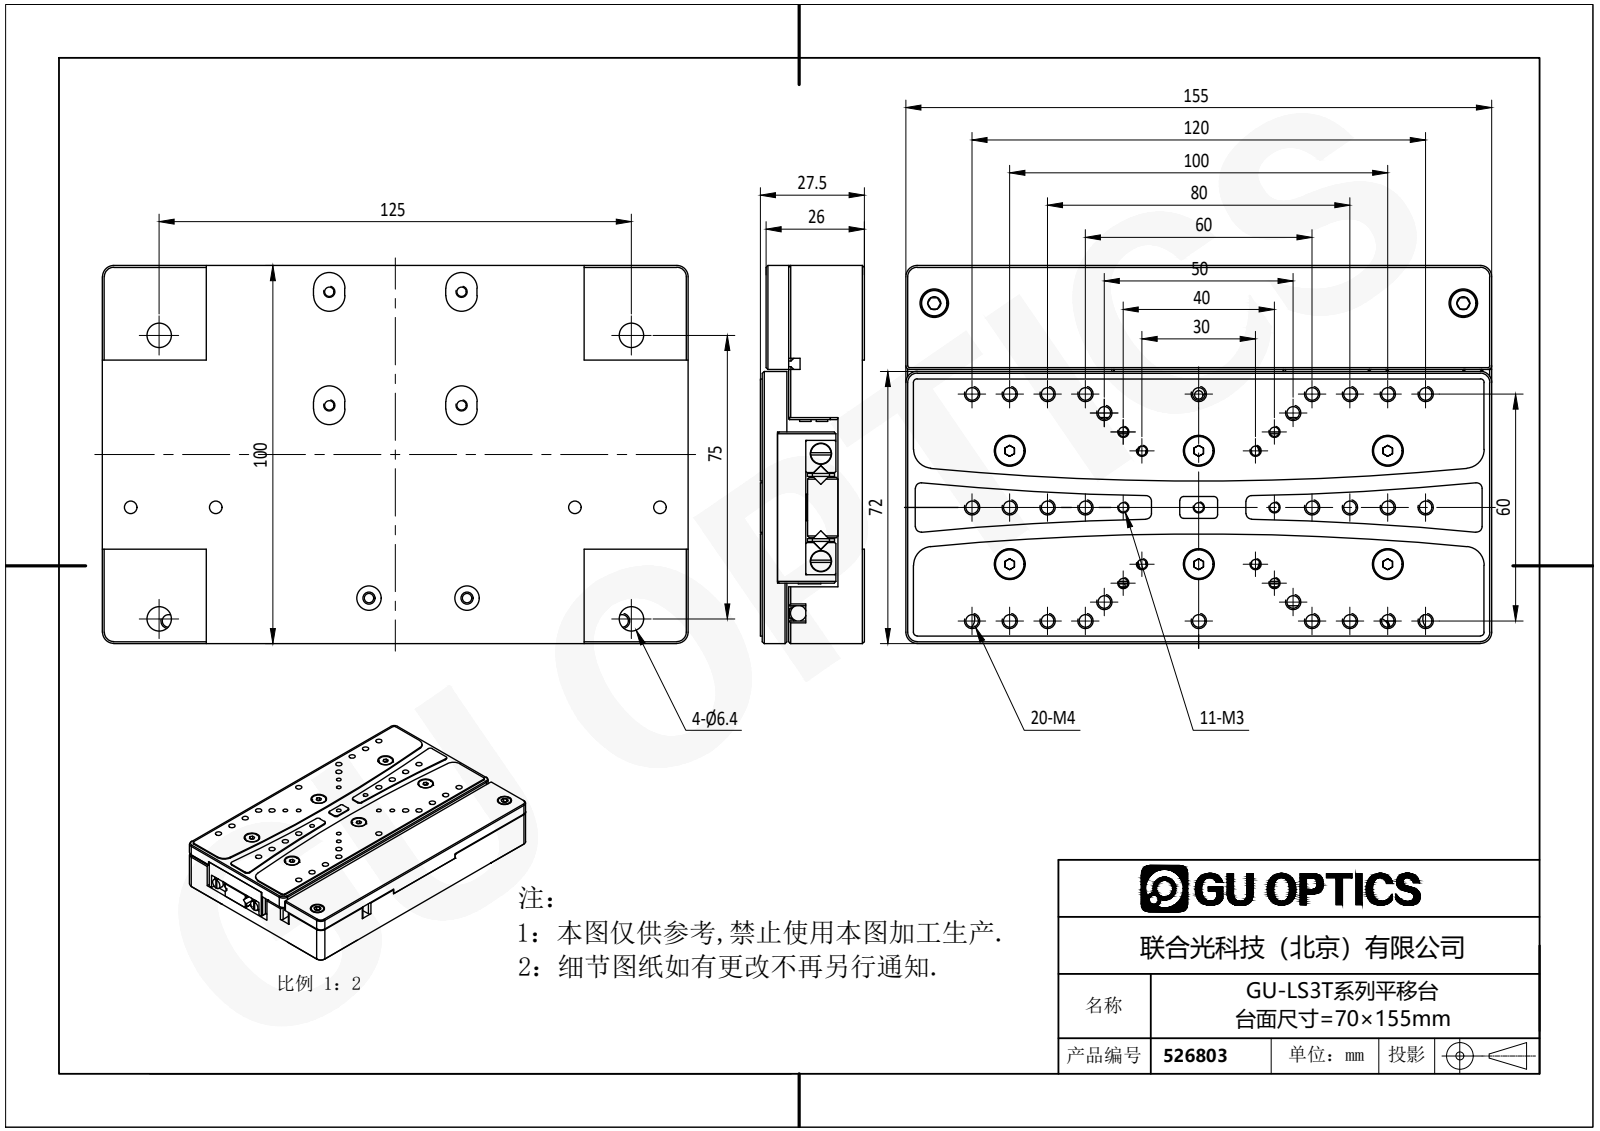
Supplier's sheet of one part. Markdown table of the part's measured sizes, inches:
| quantity | value |
| --- | --- |
| part name | GU-LS3T系列平移台 台面尺寸=70×155mm |
| STEP written by | SolidWorks 2019 (AUTOMOTIVE_DESIGN) |
| units | inches |
| bodies | 0 solids, 1836 faces (795 planar, 584 cylindrical, 457 other) |
| overall size | 6.102 × 3.937 × 1.083 |
| round holes (diameter × count) | 0.13 × 36, 0.157 × 36, 0.098 × 23, 0.118 × 23, 0.295 × 18, 0.213 × 12, 0.169 × 8, 0.062 × 6, 0.128 × 6, 0.323 × 6, 0.177 × 4, 0.252 × 4 |
| round bosses / shafts (diameter × count) | 0.276 × 18, 0.157 × 18, 0.296 × 6, 0.128 × 6, 0.218 × 4 |
| partial cylindrical surfaces (radius × count) | 0.039 × 15, 0.059 × 9, 0.118 × 8, 0.122 × 8, 0.197 × 7, 0.102 × 4, 0.069 × 2, 0.089 × 2 |
| main face-to-face distances | 0.295, 0.02, 0.63, 0.256, 0.276, 0.177, 0.787, 0.118, 0.512, 0.807 |
| hole center spacings | 0.984, 1.969, 2.953, 0.335, 3.937, 4.921, 2.053, 2.709 |
